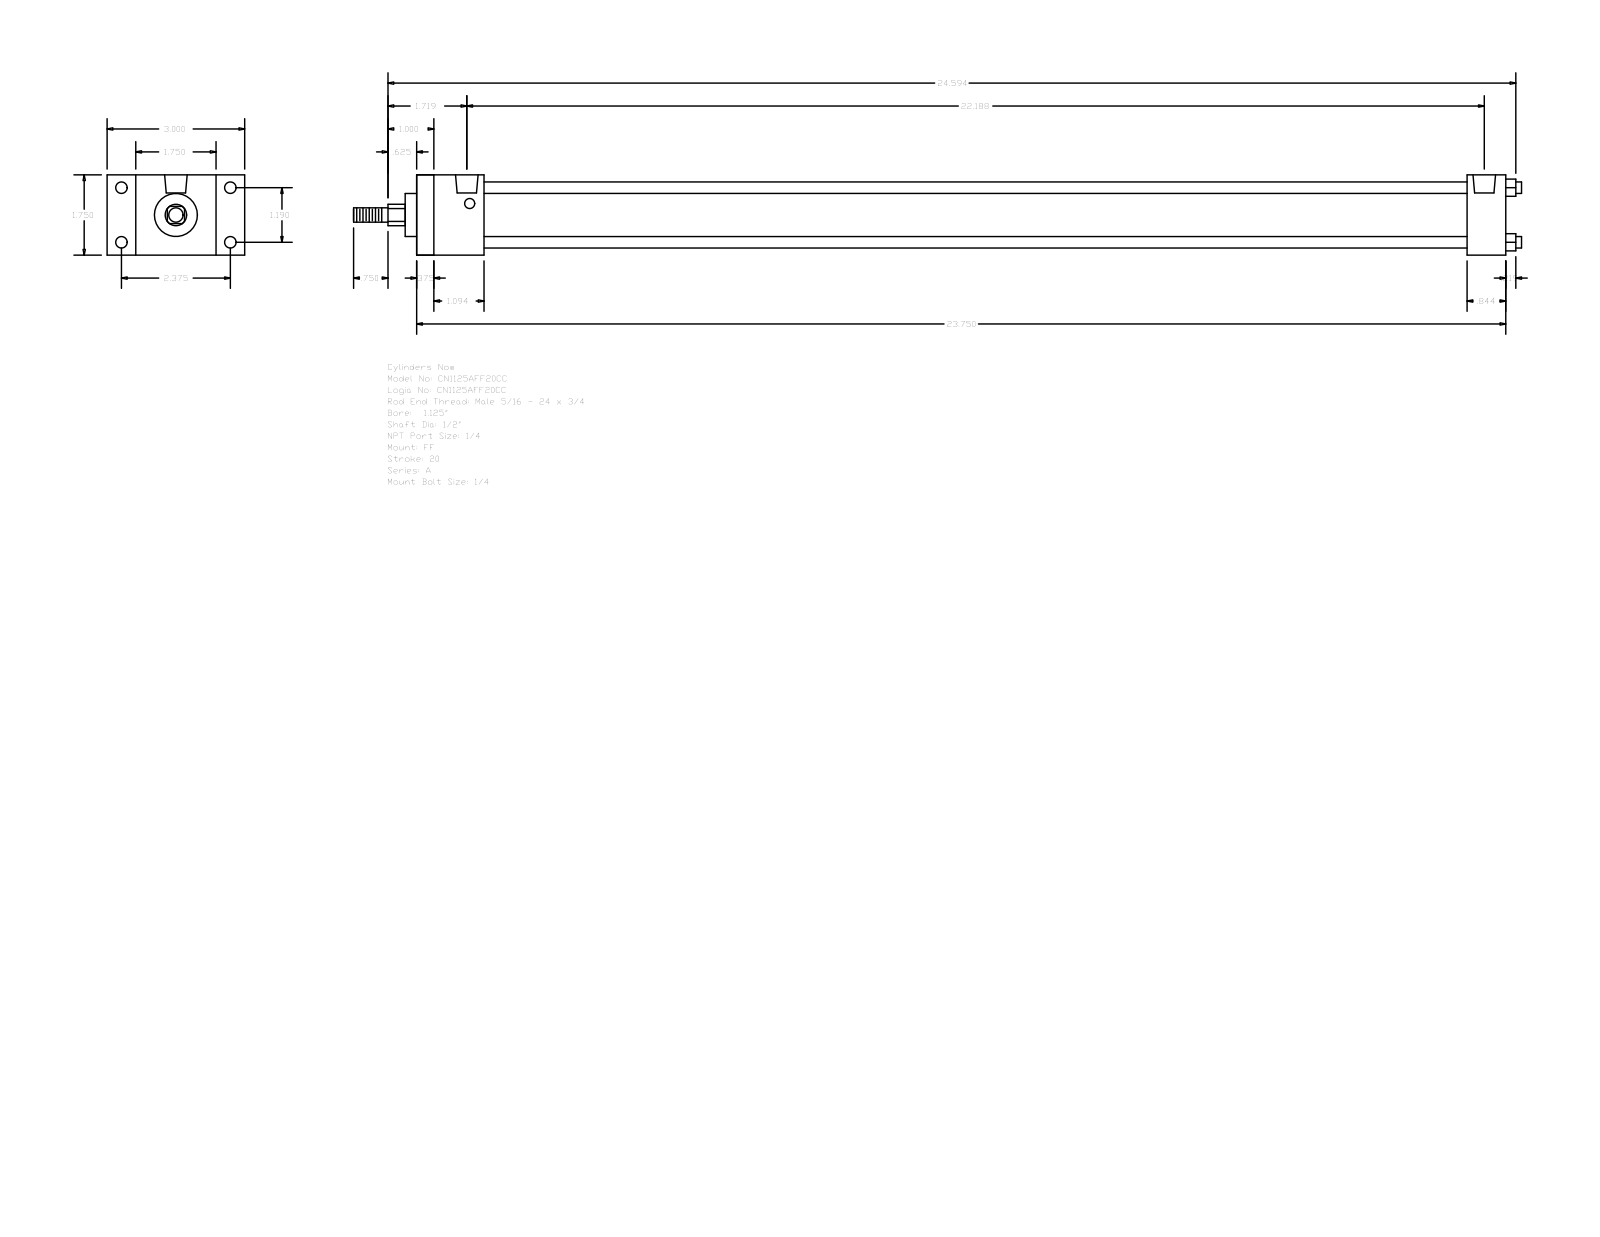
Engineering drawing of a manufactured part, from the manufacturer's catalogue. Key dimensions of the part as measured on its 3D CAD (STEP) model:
Part name (STEP PRODUCT): A_FF__0112_0.5
STEP written by: GSSL Pune (CONFIG_CONTROL_DESIGN)
Units: millimetres
Bodies: 0 solids, 92 faces (64 planar, 28 cylindrical, 0 other)
Overall size (bounding box): 646.91 × 76.2 × 44.45
Round holes (diameter × count): ⌀5.56 ×4, ⌀6.35 ×4, ⌀12.49 ×2
Round bosses / shafts (diameter × count): ⌀6.35 ×4, ⌀31.88 ×1, ⌀23.81 ×1, ⌀12.7 ×1, ⌀7.94 ×1
Partial cylindrical surfaces — rounded edges, fillets, slot ends (radius × count): R5.94 ×1
Main face-to-face distances: 44.46, 603.24, 9.52, 593.72, 15.87, 581.81, 572.29, 21.43, 37.3, 27.78
Hole centre spacings: 30.22, 60.32, 67.47, 560.39, 1.58, 1.59, 561.97, 561.98
